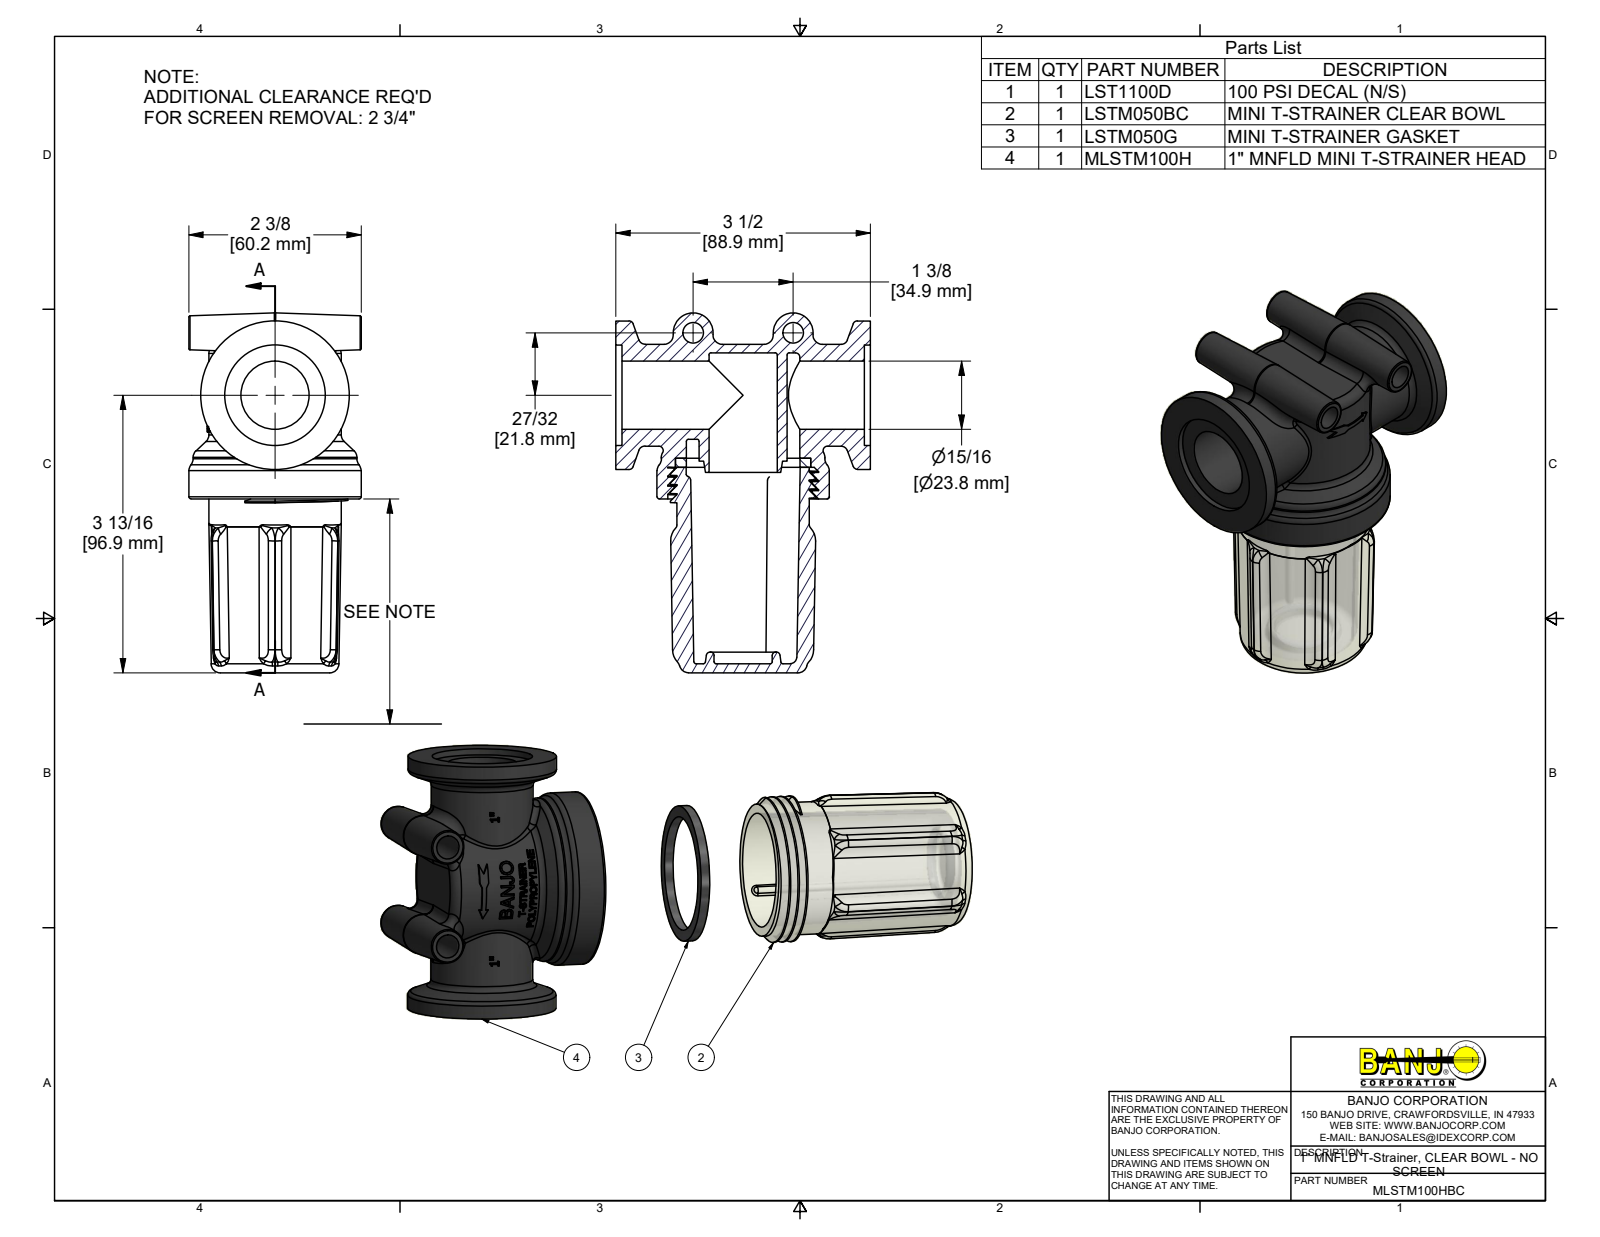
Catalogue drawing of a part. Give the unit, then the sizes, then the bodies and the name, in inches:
Units: inches
Overall size (bounding box): 4.947 × 3.5 × 2.37
Round holes (diameter × count): ⌀0.937 ×2, ⌀0.8 ×1, ⌀1.38 ×1, ⌀1.56 ×1, ⌀1.563 ×1, ⌀1.891 ×1, ⌀2.073 ×1
Round bosses / shafts (diameter × count): ⌀2.37 ×1, ⌀2.25 ×1, ⌀2.04 ×1, ⌀2.001 ×1, ⌀1.861 ×1, ⌀1.86 ×1, ⌀1.82 ×1, ⌀1.4 ×1
Partial cylindrical surfaces — rounded edges, fillets, slot ends (radius × count): R0.03 ×4, R0.05 ×3, R0.546 ×1, R0.605 ×1, R0.609 ×1, R0.73 ×1
Main face-to-face distances: 2.825, 3.5, 0.125, 0.084, 3.416, 2.95, 4.515, 1.69, 1.565, 4.397
Volume: 8.604 in³ · Surface area: 110.8 in²
Bodies: 3 solids, 786 faces (298 planar, 96 cylindrical, 392 other)
Part name (STEP PRODUCT): MLSTM100HBC; MLSTM100H; LSTM050G; LSTM050BC
STEP written by: Autodesk Inventor 2019 (AUTOMOTIVE_DESIGN)
